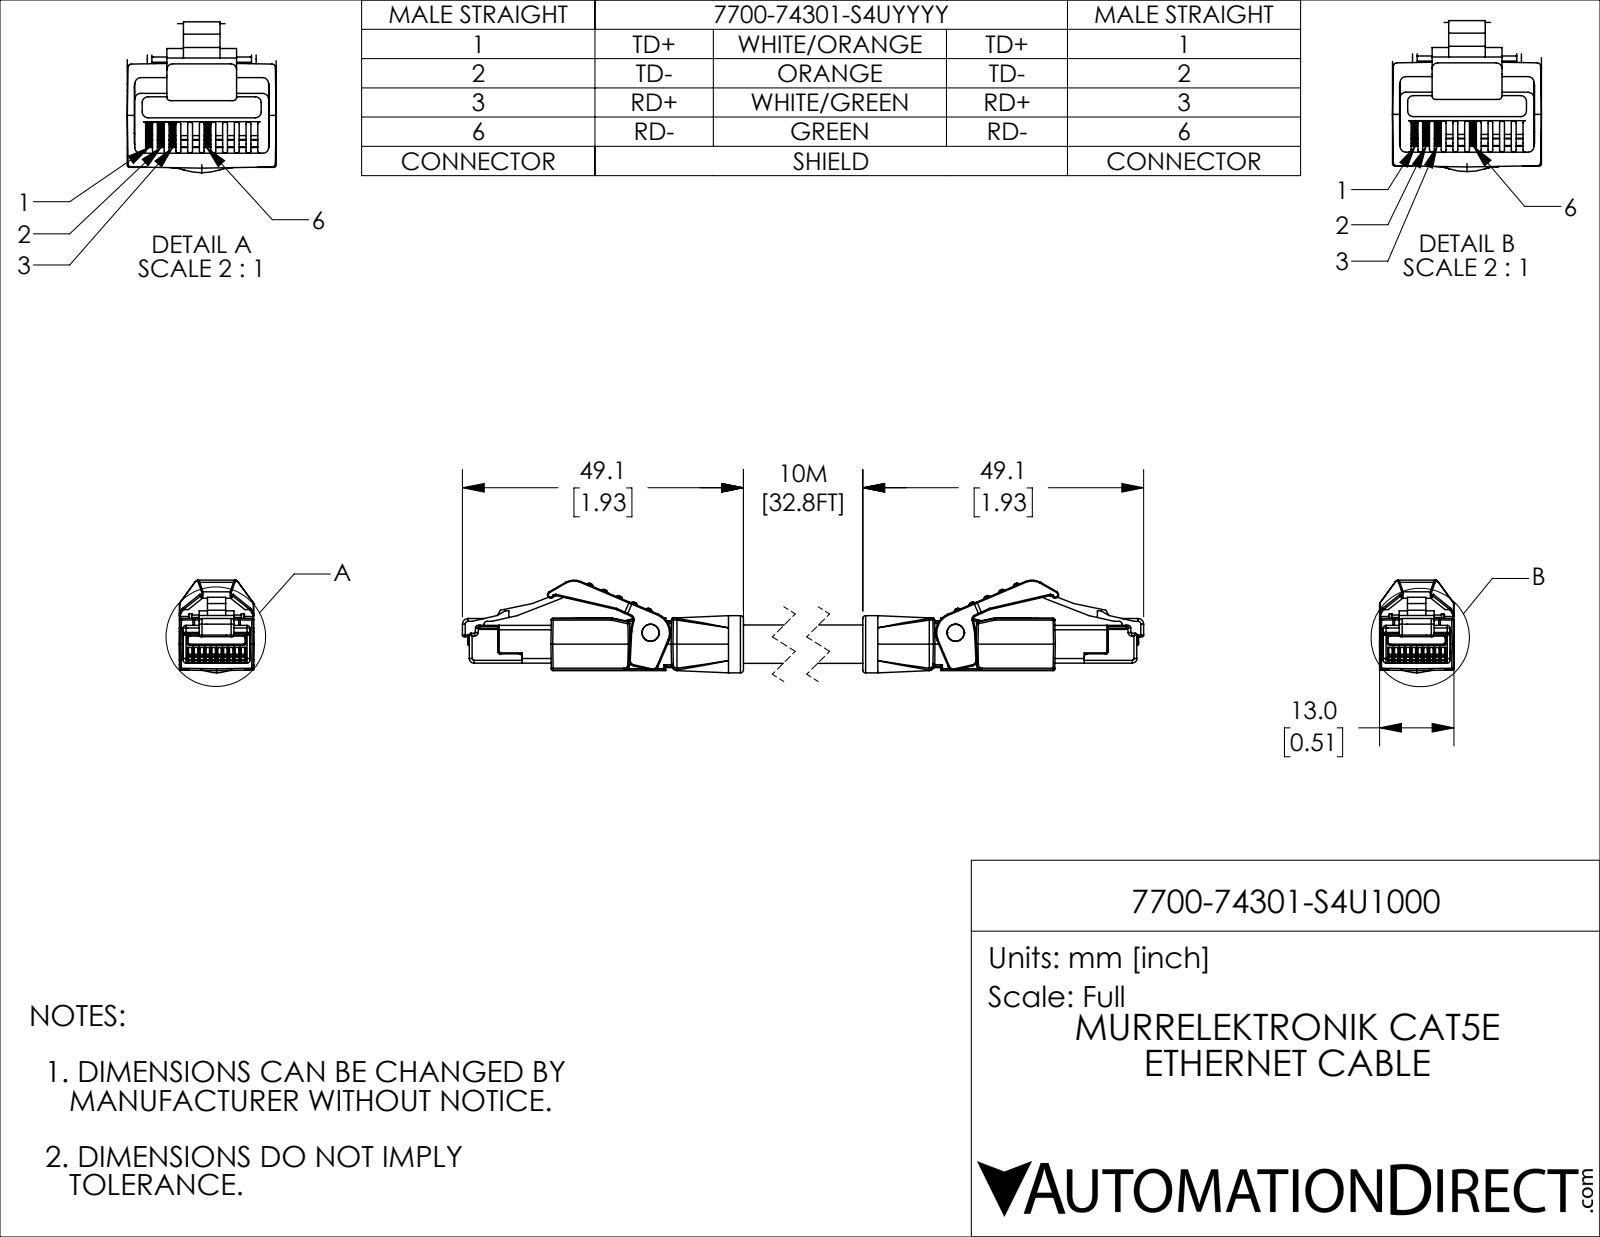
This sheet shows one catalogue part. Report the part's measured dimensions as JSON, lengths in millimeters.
{"part_name": "7700-74301-S4U1000_1; 7700-74301-S4U1000", "step_written_by": "SolidWorks 2021 (CONFIG_CONTROL_DESIGN)", "units": "millimeters", "bodies": {"solids": 2, "faces": 1406, "planar": 568, "cylindrical": 566, "other": 272}, "overall_size": [129.8, 16.2, 13], "volume_mm3": 10900, "surface_area_mm2": 6981, "round_holes": [[3, 2]], "round_bosses_or_shafts": [[3, 2], [10, 1], [6.7, 1]], "partial_cylinders_radius": [[0.2, 136], [0.3, 114], [0.1, 40], [0.5, 36], [1, 10], [0.8, 6], [2, 4], [5, 4]], "face_to_face_distances": [13, 9.2, 0.6, 12.4, 0.7, 6.6, 1.8, 11.3, 1.1, 10.6], "hole_center_spacings": [64.2]}
